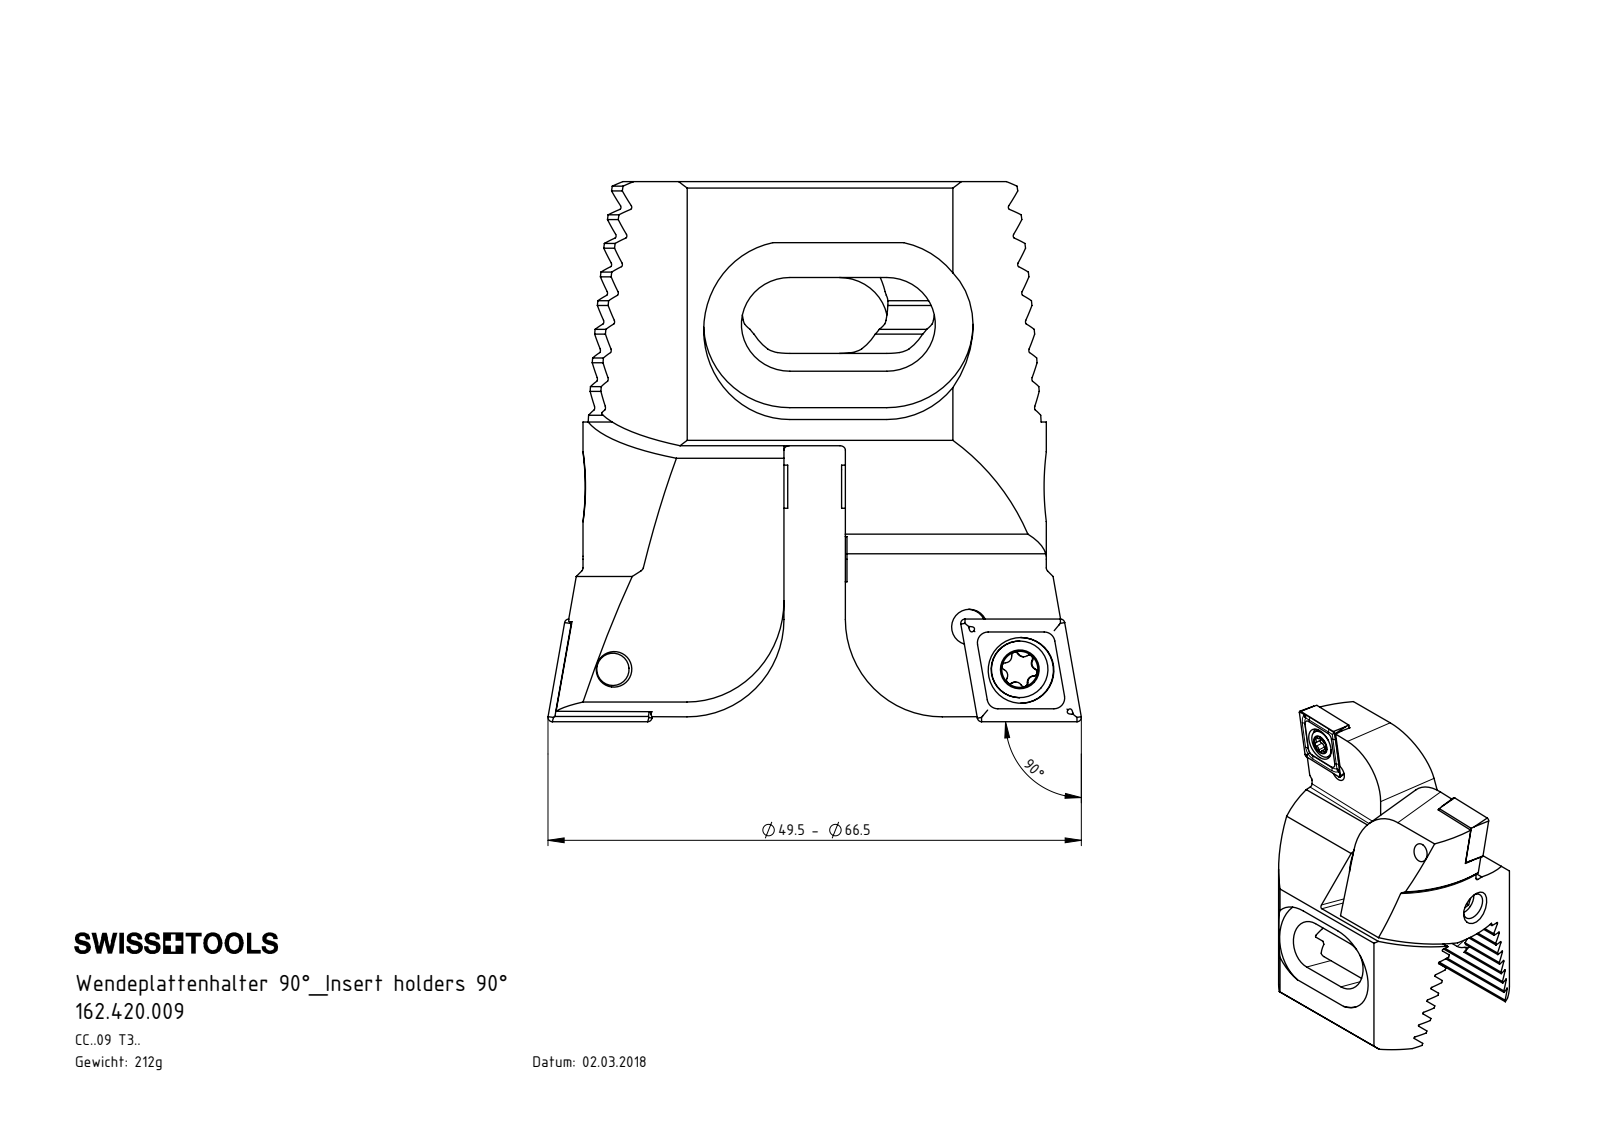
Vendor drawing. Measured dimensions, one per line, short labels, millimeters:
name: Z42-WCB.001.028_A; WCB-ER2.001.009_A; 162.420.009; Z42-ER3.001.016 (+1 more)
written by: SolidWorks 2017 (CONFIG_CONTROL_DESIGN)
unit: mm
bodies: 8 solids, 460 faces (184 planar, 152 cylindrical, 124 other)
size: 50.1 × 49.5 × 34.2
volume: 26 971 mm³; area: 13 466 mm²
holes: 4× ⌀3.3, 2× ⌀1, 2× ⌀4.4, 2× ⌀6.1, 1× ⌀5
bosses: 3× ⌀4, 2× ⌀5.25, 1× ⌀6
rounds: 16× R0.2, 12× R0.34, 12× R0.59, 8× R1, 4× R0.5, 4× R4.5, 4× R8, 2× R9
face distances: 2.38, 4.76, 11.91, 9.53, 14.29, 7.15, 4.99, 7.14, 1.04, 16.67
hole spacings: 6.1, 13, 33.59, 6.25, 6.26, 25.12, 28.69, 33.71
